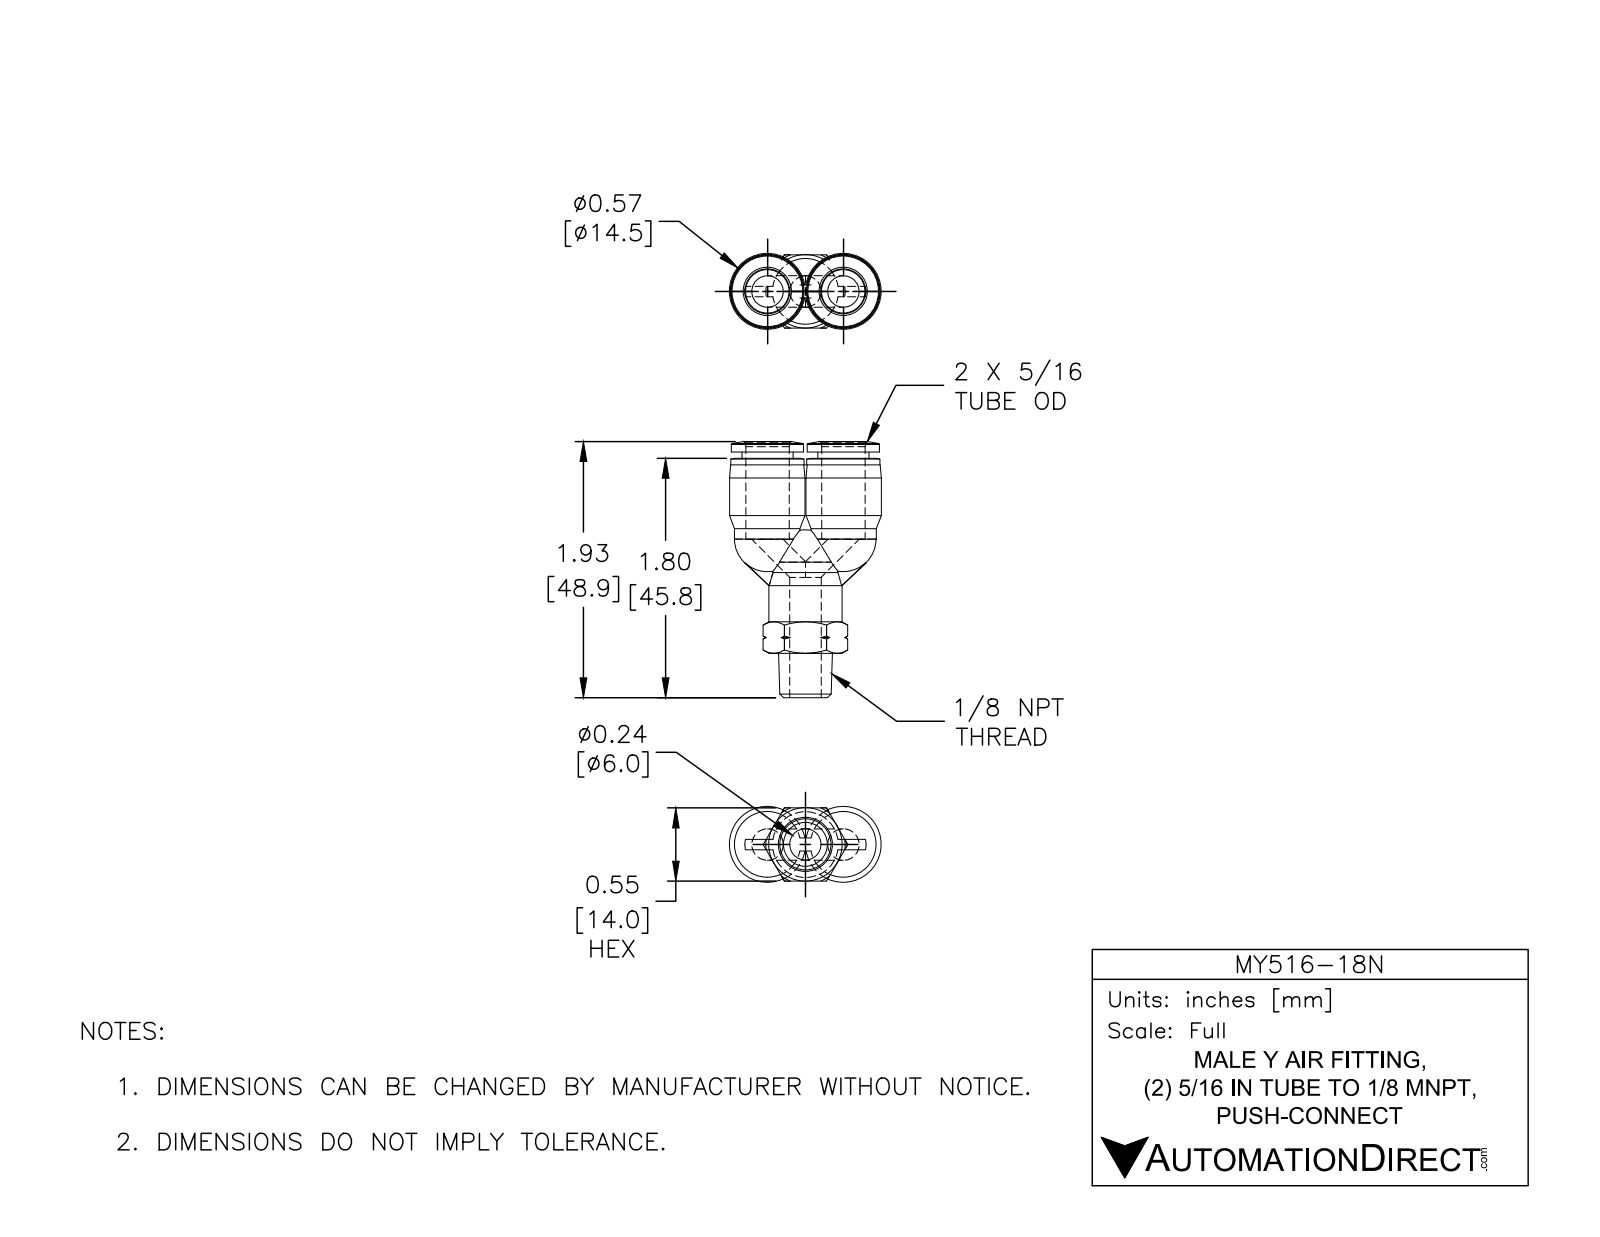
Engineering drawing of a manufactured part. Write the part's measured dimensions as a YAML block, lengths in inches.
part_name: "MY516-18N"
step_written_by: "SolidWorks 2015 (CONFIG_CONTROL_DESIGN)"
units: inches
bodies: {solids: 1, faces: 126, planar: 21, cylindrical: 31, other: 74}
overall_size: [1.927, 1.142, 0.571]
volume: 0.434
surface_area: 8.308
round_holes:
  - {diameter: 0.327, count: 2}
  - {diameter: 0.236, count: 1}
round_bosses_or_shafts:
  - {diameter: 0.551, count: 3}
  - {diameter: 0.496, count: 3}
  - {diameter: 0.571, count: 2}
  - {diameter: 0.543, count: 2}
  - {diameter: 0.386, count: 2}
face_to_face_distances: [0.551, 0.047, 1.467, 1.514, 0.856, 0.61, 0.657, 0.335, 1.191, 1.801]
hole_center_spacings: [0.285, 0.571]
